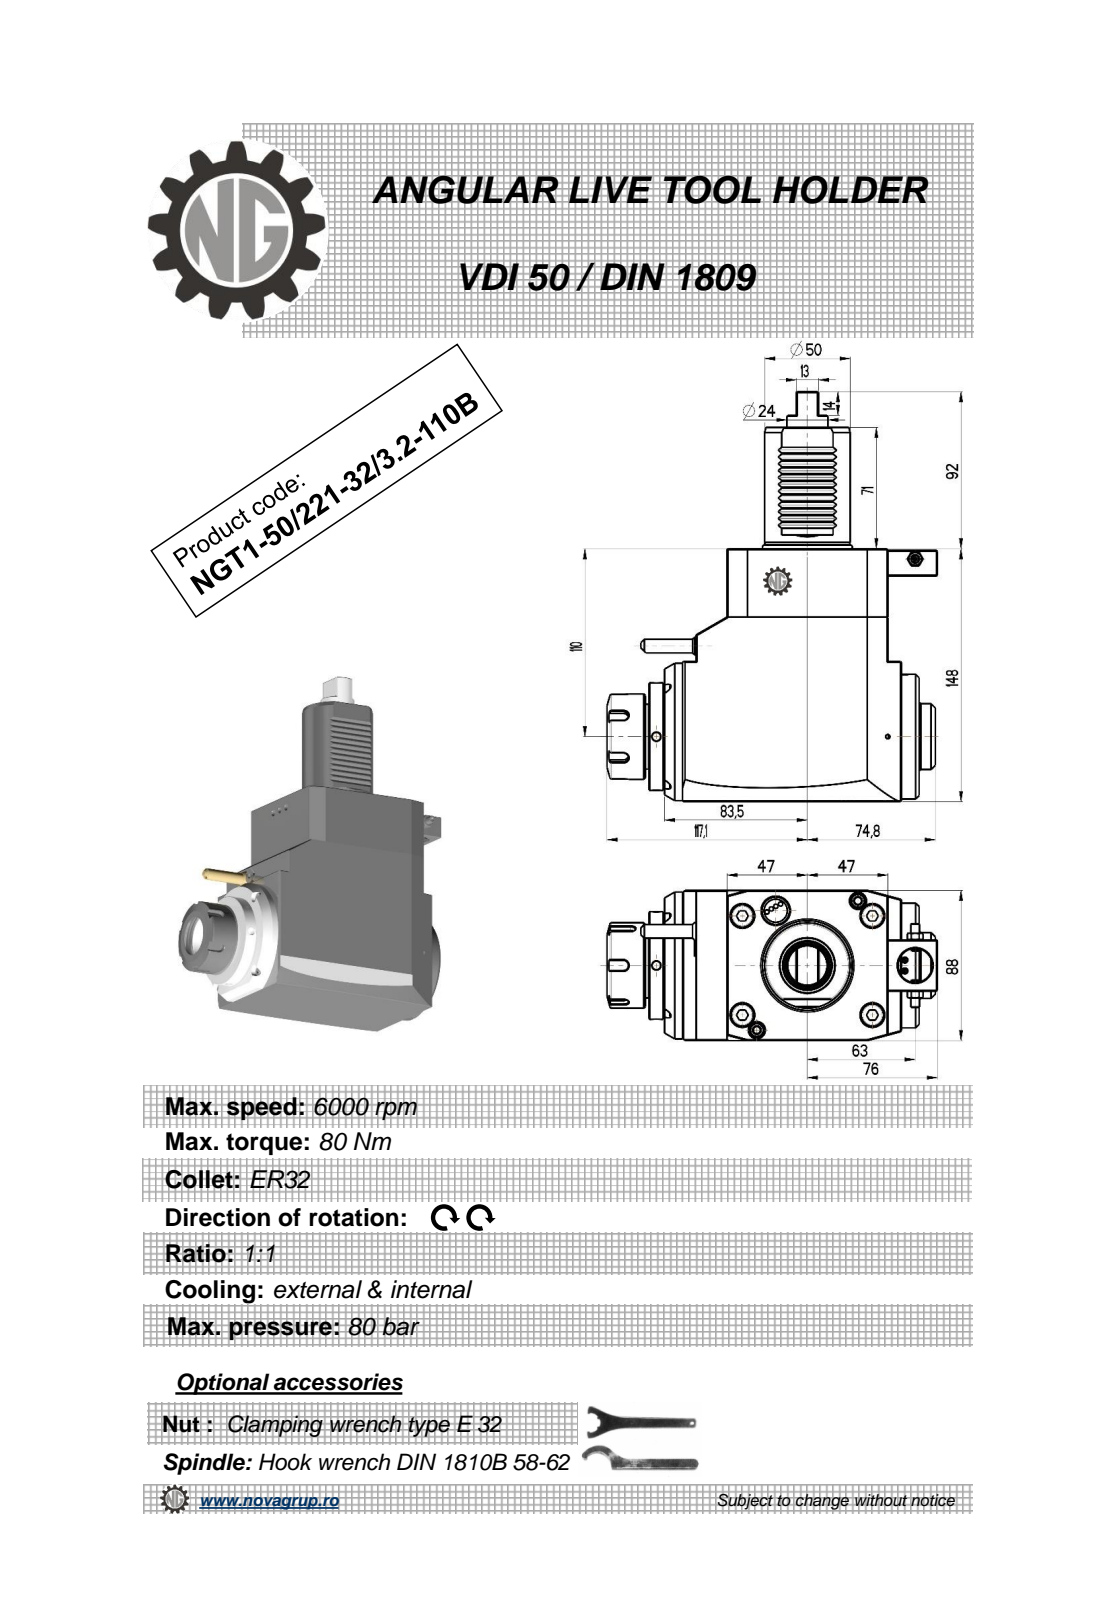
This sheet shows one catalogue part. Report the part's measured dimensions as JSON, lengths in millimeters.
{"part_name": "NGT1_50_221_32_3_2_110B", "step_written_by": "PRO/ENGINEER BY PARAMETRIC TECHNOLOGY CORPORATION, 2010280 (CONFIG_CONTROL_DESIGN)", "units": "millimeters", "bodies": {"solids": 1, "faces": 423, "planar": 198, "cylindrical": 98, "other": 127}, "overall_size": [240, 193.1, 88], "volume_mm3": 1814000, "surface_area_mm2": 112723, "round_holes": [[5, 3], [3.8, 2], [4, 2], [3, 1], [9.5, 1], [20, 1], [27, 1]], "round_bosses_or_shafts": [[50, 2], [86, 1], [73, 1], [63, 1], [50.5, 1], [41, 1], [40, 1], [38.5, 1]], "partial_cylinders_radius": [[0.26, 12], [0.3, 12], [0.2, 6], [3, 5], [0.8, 2]], "face_to_face_distances": [88, 148, 8, 94, 36.5, 130.5, 120, 148.8, 112.3, 18.3], "hole_center_spacings": [9, 101.9, 18, 49.73, 52.46, 56.51, 56.65, 101.5]}
